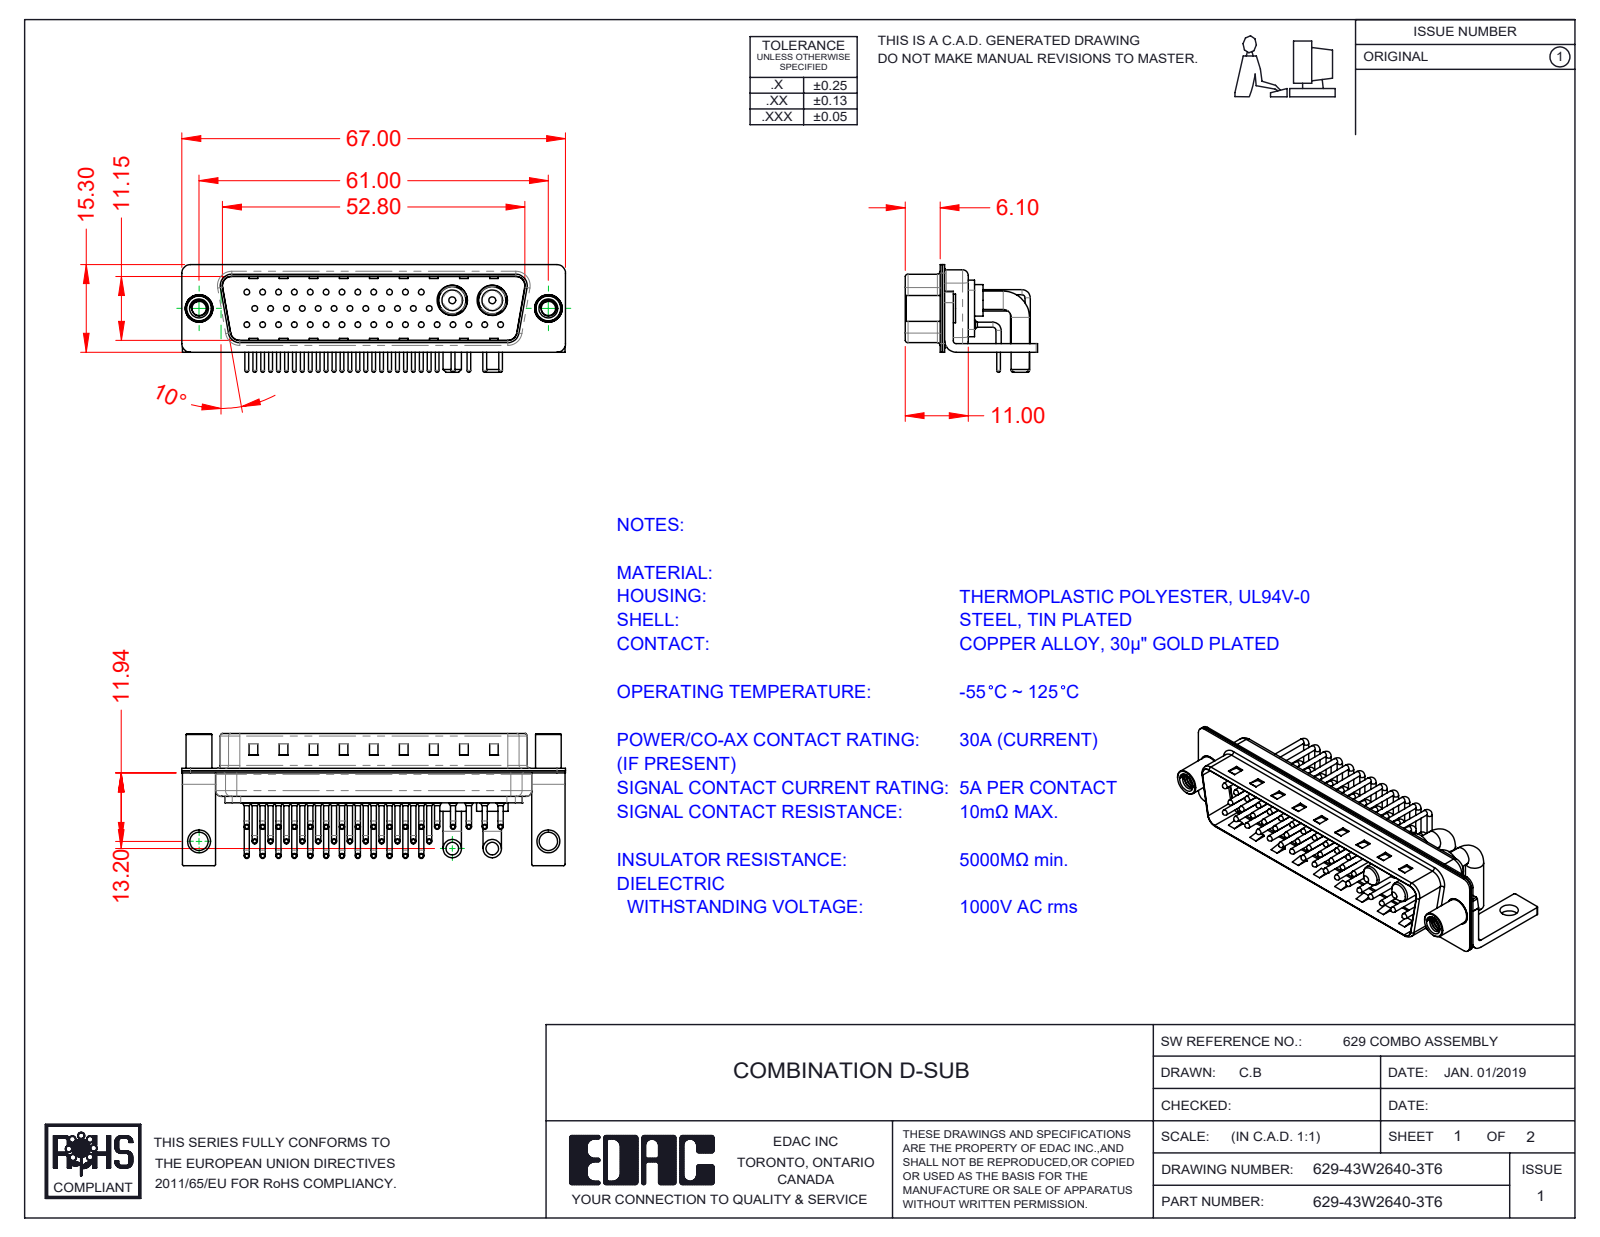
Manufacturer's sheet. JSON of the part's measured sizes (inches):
{"part_name": "629-43W2640-3T6; 629Combo Housing_43W2; 629Combo Threaded Standoff_D; 629Combo Shell Rear_50 Contacts (+6 more)", "step_written_by": "SolidWorks 2020 (CONFIG_CONTROL_DESIGN)", "units": "inches", "bodies": {"solids": 52, "faces": 5106, "planar": 2869, "cylindrical": 1731, "other": 506}, "overall_size": [2.638, 0.909, 0.74], "volume_in3": 0.35, "surface_area_in2": 21.19, "round_holes": [[0.03, 41], [0.063, 41], [0.079, 41], [0.098, 2], [0.126, 2], [0.157, 2], [0.189, 2], [0.191, 2], [0.209, 2]], "round_bosses_or_shafts": [[0.035, 82], [0.059, 41], [0.039, 41], [0.026, 41], [0.126, 4], [0.217, 2], [0.205, 2], [0.197, 2]], "partial_cylinders_radius": [[0.04, 41], [0.01, 16], [0.059, 16], [0.079, 13], [0.02, 9], [0.063, 8], [0.024, 4], [0.026, 4]], "face_to_face_distances": [0.016, 0.059, 0.455, 0.22, 0.205, 0.031, 0.075, 0.161, 0.236, 0.031], "hole_center_spacings": [0.109, 0.218, 0.124, 0.327, 0.436, 0.545, 0.654, 0.763]}
